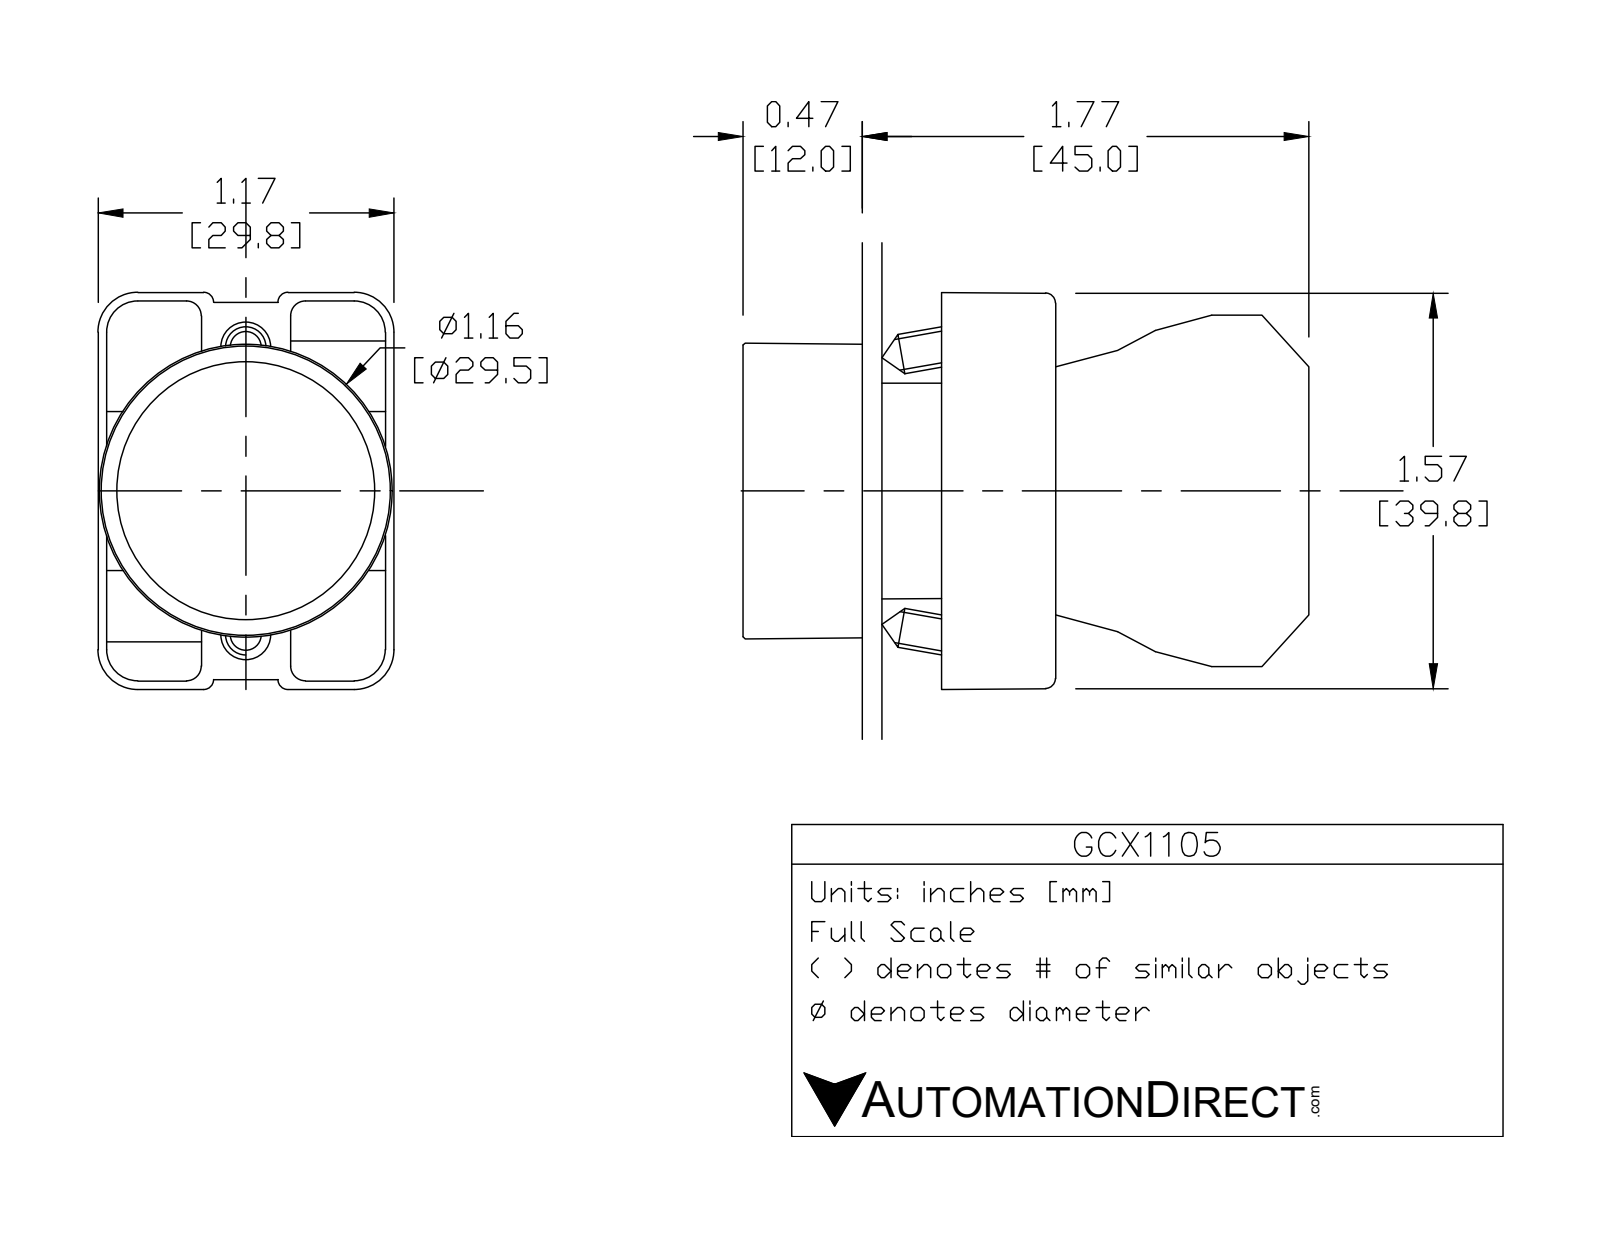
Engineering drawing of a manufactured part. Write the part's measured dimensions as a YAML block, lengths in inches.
part_name: "ecx1029; ecx1040; GCX1105 OPERATOR; GCX1105"
step_written_by: "SolidWorks 2016 (AUTOMOTIVE_DESIGN)"
units: inches
bodies: {solids: 6, faces: 381, planar: 222, cylindrical: 132, other: 27}
overall_size: [2.217, 1.581, 1.177]
volume: 1.741
surface_area: 27.14
round_holes:
  - {diameter: 0.079, count: 2}
  - {diameter: 0.124, count: 2}
  - {diameter: 0.13, count: 2}
  - {diameter: 0.087, count: 1}
  - {diameter: 0.197, count: 1}
  - {diameter: 0.878, count: 1}
  - {diameter: 0.888, count: 1}
  - {diameter: 1.024, count: 1}
round_bosses_or_shafts:
  - {diameter: 0.157, count: 2}
  - {diameter: 1.175, count: 1}
  - {diameter: 1.004, count: 1}
  - {diameter: 0.945, count: 1}
  - {diameter: 0.856, count: 1}
  - {diameter: 0.78, count: 1}
partial_cylinders:
  - {radius: 0.059, count: 24}
  - {radius: 0.041, count: 12}
  - {radius: 0.124, count: 12}
  - {radius: 0.157, count: 12}
  - {radius: 0.039, count: 4}
  - {radius: 0.128, count: 2}
  - {radius: 0.02, count: 1}
  - {radius: 0.063, count: 1}
face_to_face_distances: [0.72, 0.579, 0.033, 0.472, 1.193, 0.031, 0.689, 0.598, 1.161, 1.071]
hole_center_spacings: [0.236, 0.544, 0.472, 0.49]
